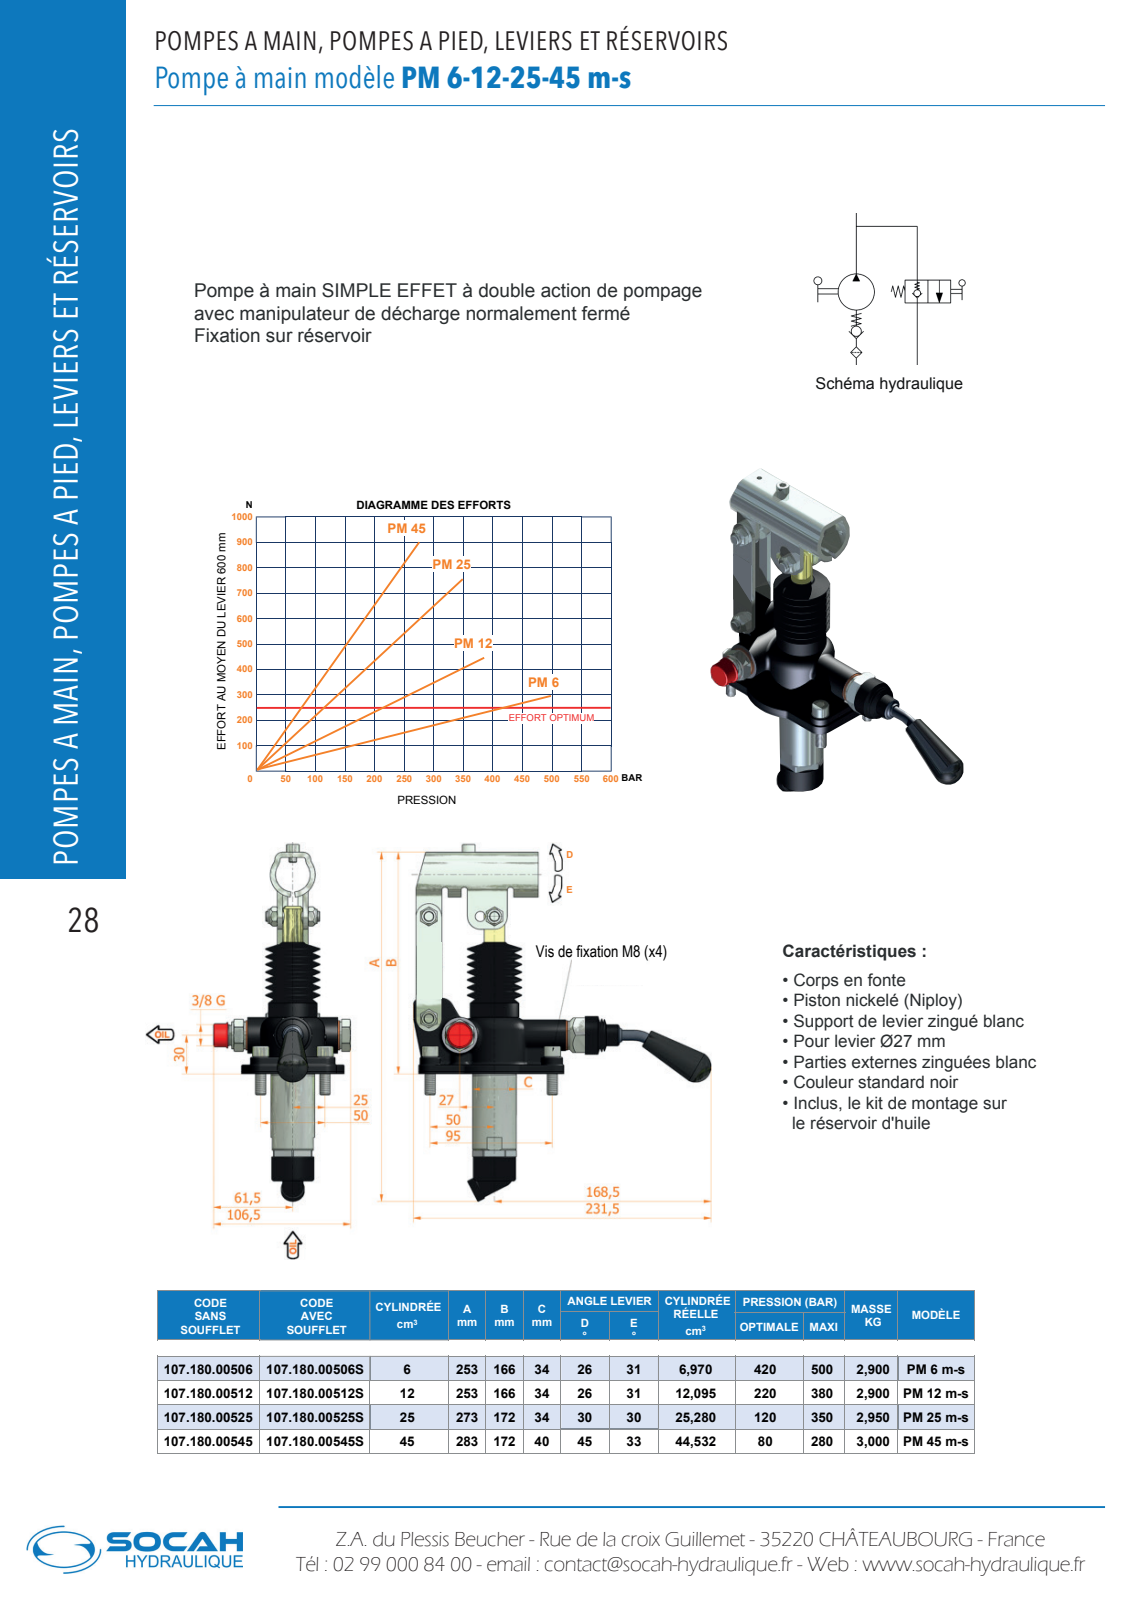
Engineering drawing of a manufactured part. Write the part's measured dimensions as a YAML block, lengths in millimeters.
part_name: "Parte38"
step_written_by: "Autodesk Inventor 2013 (AUTOMOTIVE_DESIGN)"
units: millimeters
bodies: {solids: 7, faces: 1501, planar: 691, cylindrical: 323, other: 487}
overall_size: [277.85, 231.44, 106.5]
round_holes:
  - {diameter: 8, count: 5}
  - {diameter: 14, count: 4}
  - {diameter: 8.5, count: 2}
  - {diameter: 10, count: 2}
  - {diameter: 25, count: 2}
  - {diameter: 4, count: 1}
  - {diameter: 5, count: 1}
  - {diameter: 9, count: 1}
  - {diameter: 13.47, count: 1}
  - {diameter: 16, count: 1}
  - {diameter: 17, count: 1}
  - {diameter: 21, count: 1}
round_bosses_or_shafts:
  - {diameter: 8, count: 6}
  - {diameter: 13, count: 4}
  - {diameter: 12, count: 4}
  - {diameter: 18, count: 3}
  - {diameter: 11.05, count: 3}
  - {diameter: 23, count: 2}
  - {diameter: 20, count: 2}
  - {diameter: 16, count: 2}
partial_cylinders:
  - {radius: 1, count: 25}
  - {radius: 0.2, count: 24}
  - {radius: 3, count: 17}
  - {radius: 0.1, count: 16}
  - {radius: 2, count: 16}
  - {radius: 8, count: 9}
  - {radius: 0.36, count: 6}
  - {radius: 0.53, count: 6}
face_to_face_distances: [4, 20, 16, 2, 5, 7, 24, 1, 26, 31]
hole_center_spacings: [25.5, 26.1, 26.93, 50, 51.48, 55.9, 88.6, 91]
